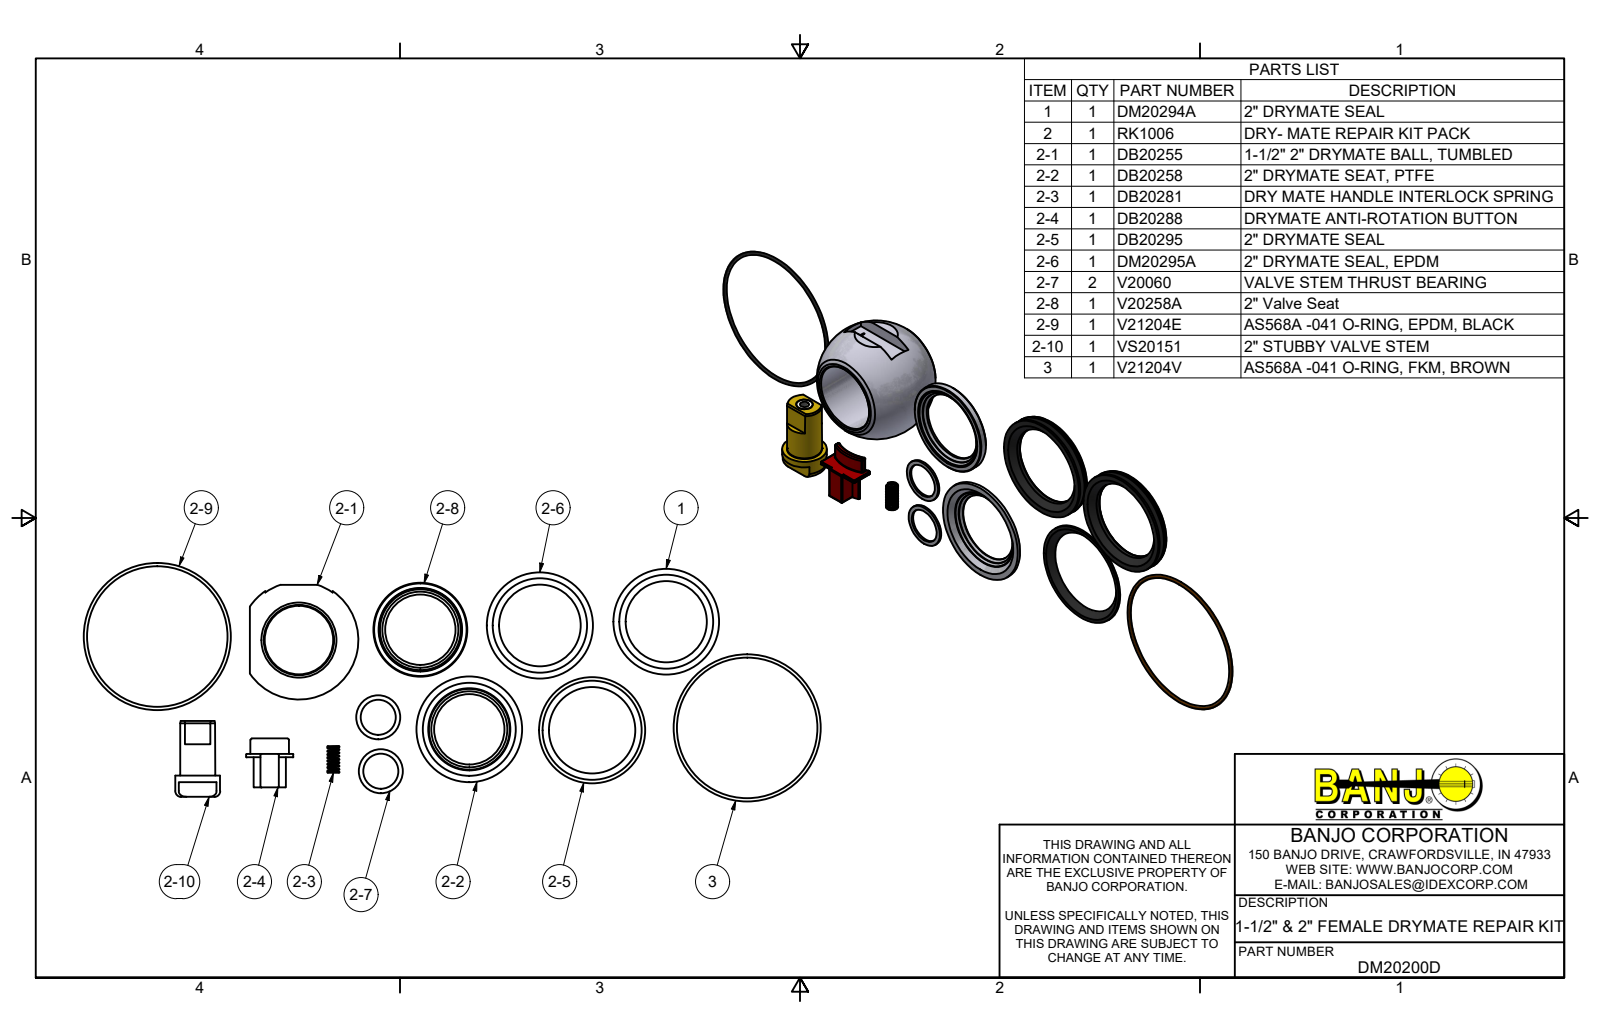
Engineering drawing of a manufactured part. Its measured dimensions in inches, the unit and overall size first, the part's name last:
Units: inches
Overall size (bounding box): 15.663 × 5.068 × 1.91
Round holes (diameter × count): ⌀2.15 ×3, ⌀0.75 ×2, ⌀1.5 ×2, ⌀1.616 ×2, ⌀1.73 ×2, ⌀0.196 ×1, ⌀0.351 ×1, ⌀0.375 ×1, ⌀1.455 ×1, ⌀1.566 ×1
Round bosses / shafts (diameter × count): ⌀2.25 ×4, ⌀0.937 ×2, ⌀2 ×1, ⌀1.766 ×1, ⌀0.95 ×1, ⌀0.745 ×1, ⌀0.125 ×1
Partial cylindrical surfaces — rounded edges, fillets, slot ends (radius × count): R0.02 ×20, R0.01 ×10, R0.03 ×8, R0.88 ×2, R0.135 ×1, R0.875 ×1, R0.92 ×1
Main face-to-face distances: 0.298, 0.17, 0.014, 0.272, 0.026, 0.23, 0.06, 0.139, 0.507, 0.235
Hole centre spacings: 1.143, 1.953, 2.067, 2.081, 2.35, 2.36, 2.491, 2.541
Volume: 5.827 in³ · Surface area: 73.3 in²
Bodies: 14 solids, 392 faces (127 planar, 97 cylindrical, 168 other)
Part name (STEP PRODUCT): DM20200D; DM20294A; RK1006; DB20255 (+8 more)
STEP written by: Autodesk Inventor 2022 (AUTOMOTIVE_DESIGN)
